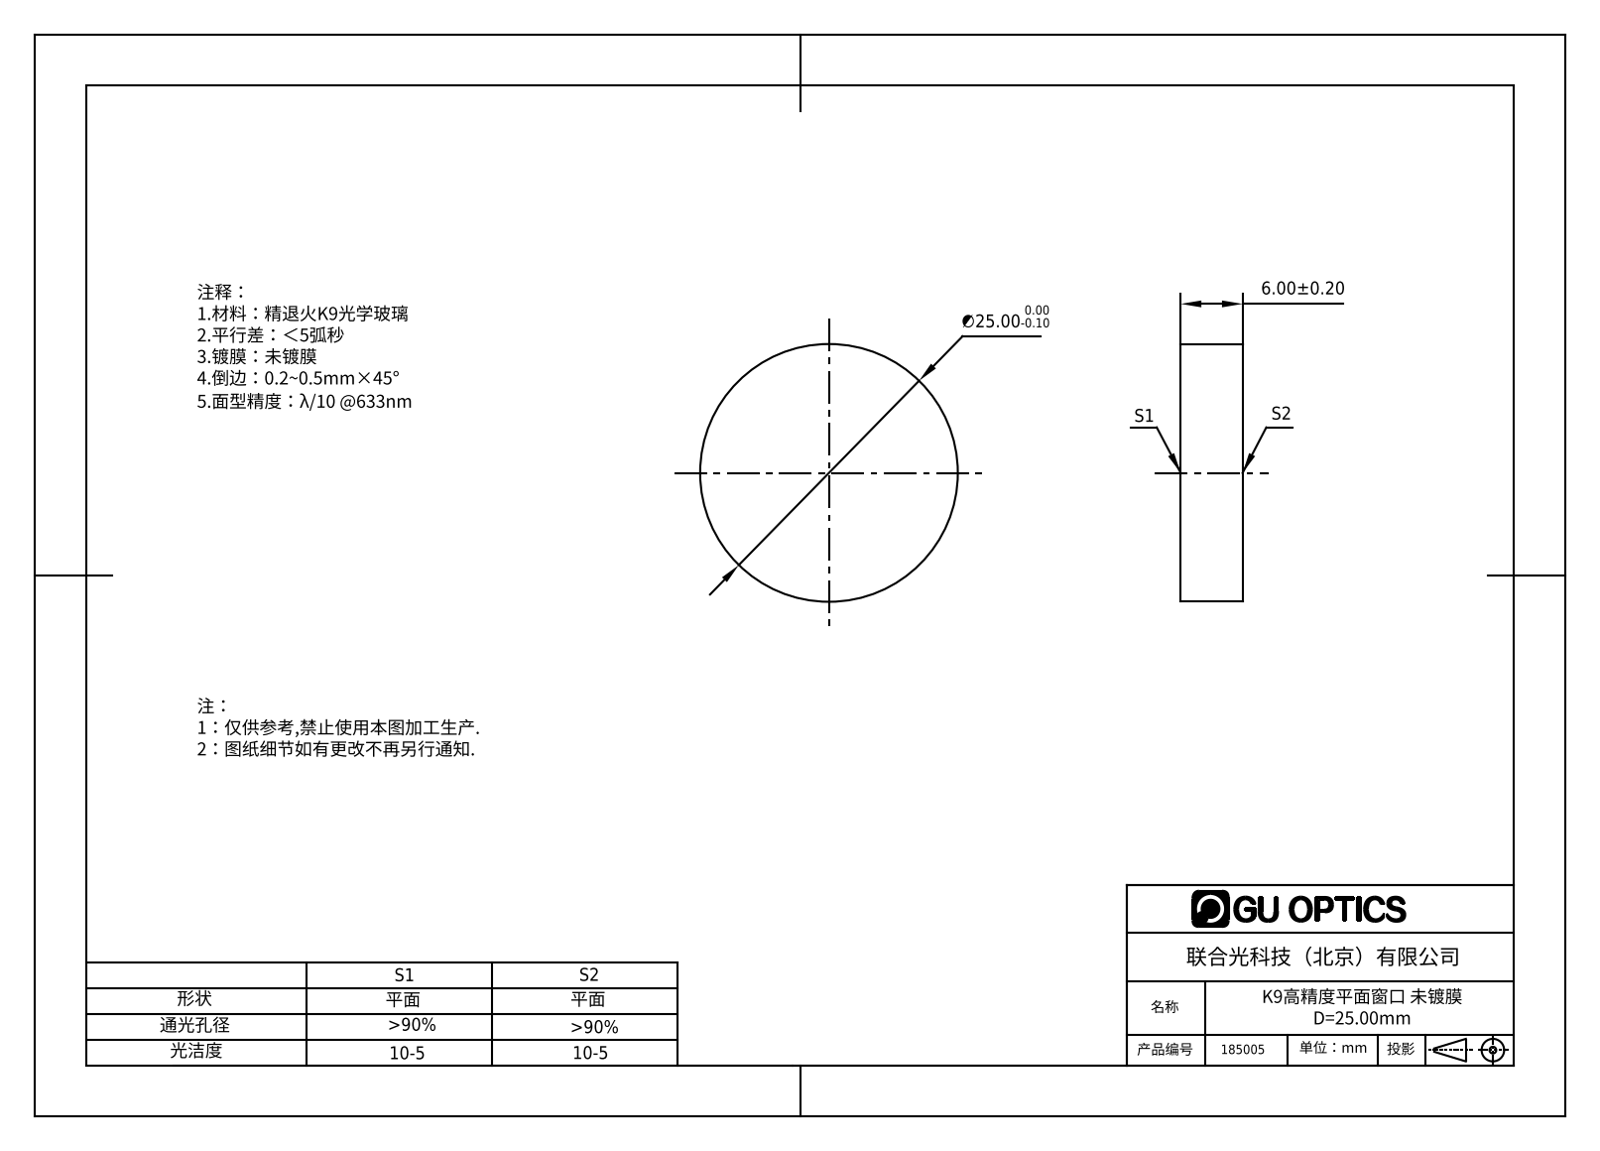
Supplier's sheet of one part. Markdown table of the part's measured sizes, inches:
| quantity | value |
| --- | --- |
| part name | 185005 |
| STEP written by | SolidWorks 2016 (AUTOMOTIVE_DESIGN) |
| units | inches |
| bodies | 1 solid, 4 faces (2 planar, 2 cylindrical, 0 other) |
| overall size | 0.984 × 0.984 × 0.236 |
| volume | 0.18 in³ |
| surface area | 2.252 in² |
| round bosses / shafts (diameter × count) | 0.984 × 1 |
| main face-to-face distances | 0.236 |
